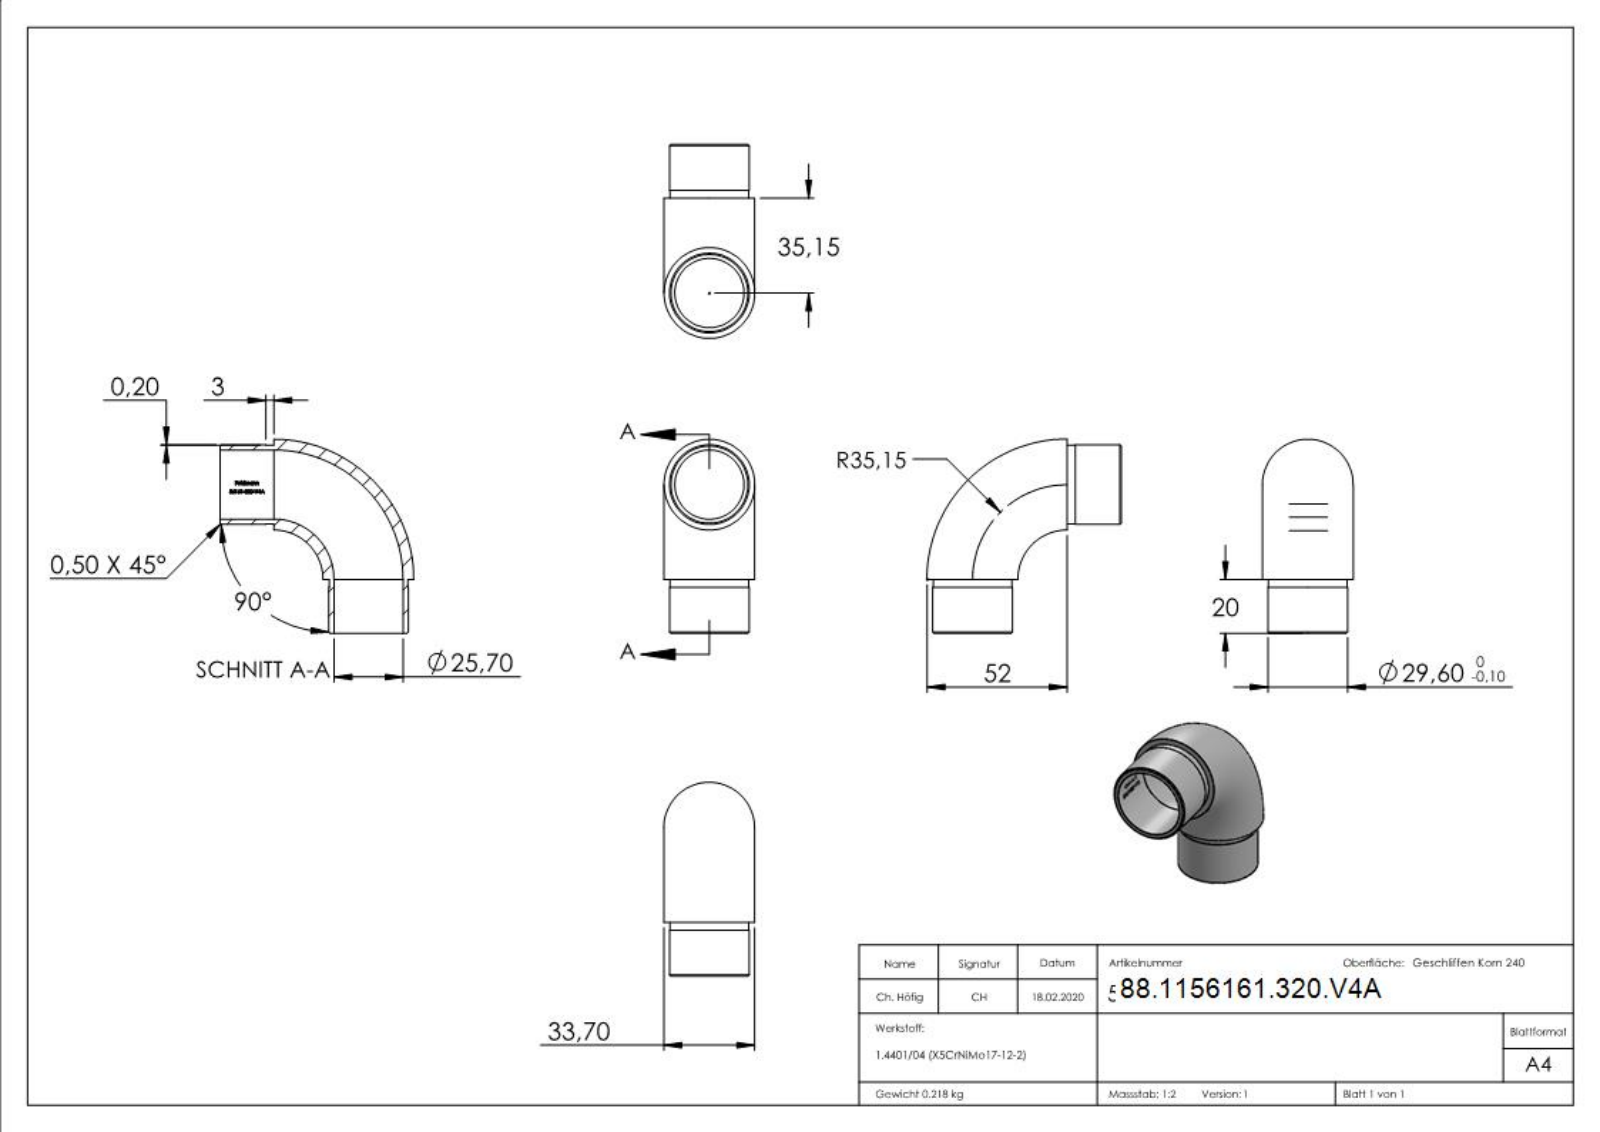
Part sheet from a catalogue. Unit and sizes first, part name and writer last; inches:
Units: inches
Overall size (bounding box): 2.835 × 2.835 × 1.327
Round holes (diameter × count): ⌀1.012 ×2
Round bosses / shafts (diameter × count): ⌀1.165 ×2, ⌀1.15 ×2
Partial cylindrical surfaces — rounded edges, fillets, slot ends (radius × count): R0.51 ×1
Main face-to-face distances: 0.787, 0.669, 0.118, 0.015, 0.054, 0.052, 0.08, 0.074, 0.144, 0.129
Volume: 1.663 in³ · Surface area: 27.93 in²
Bodies: 1 solid, 274 faces (132 planar, 35 cylindrical, 107 other)
Part name (STEP PRODUCT): 56161-320-V4A
STEP written by: SolidWorks 2015 (CONFIG_CONTROL_DESIGN)
